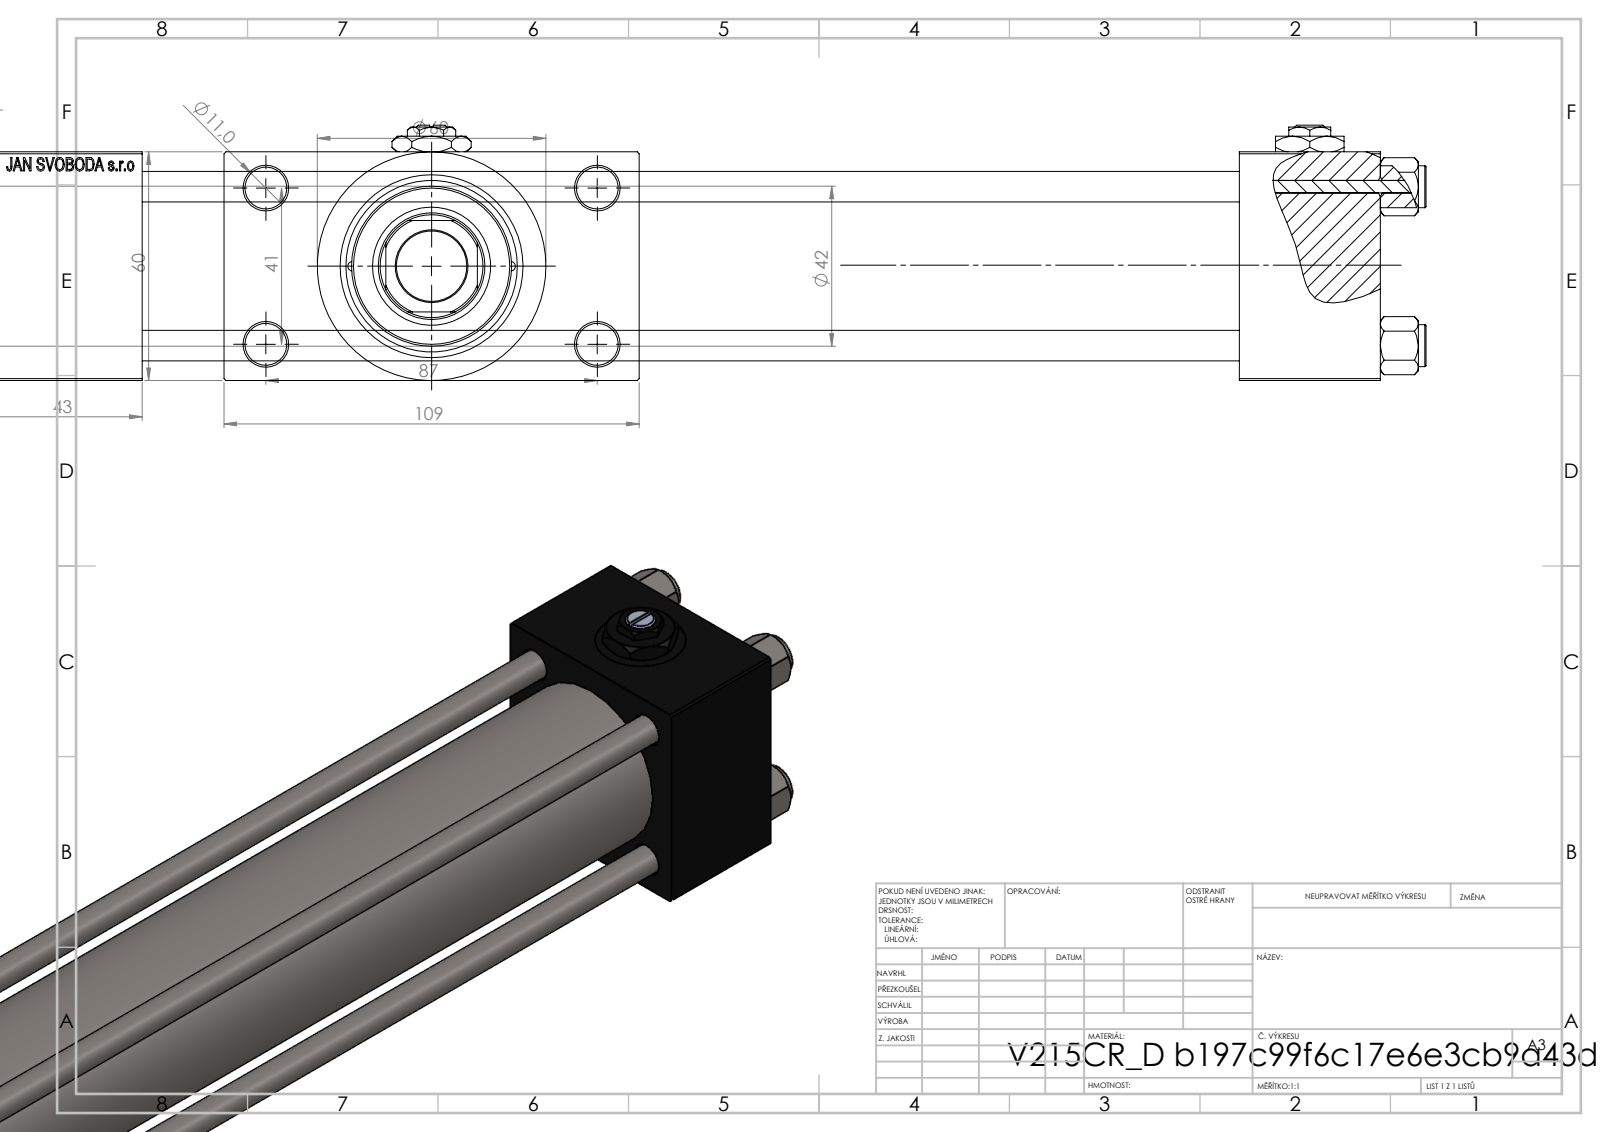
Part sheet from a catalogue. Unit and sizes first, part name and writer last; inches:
Units: inches
Overall size (bounding box): 16.339 × 4.291 × 2.638
Round holes (diameter × count): ⌀0.315 ×4, ⌀0.433 ×4, ⌀0.276 ×3, ⌀0.656 ×3, ⌀0.945 ×3, ⌀0.098 ×2, ⌀0.728 ×1, ⌀1.102 ×1, ⌀1.22 ×1, ⌀1.575 ×1, ⌀1.772 ×1
Round bosses / shafts (diameter × count): ⌀0.433 ×4, ⌀2.362 ×1, ⌀1.811 ×1, ⌀1.654 ×1
Partial cylindrical surfaces — rounded edges, fillets, slot ends (radius × count): R0.531 ×1
Main face-to-face distances: 2.362, 0.965, 11.339, 3.327, 1.457, 12.795, 14.488, 13.031, 1.693, 4.291
Hole centre spacings: 0.821, 0.892, 1.161, 1.206, 1.642, 1.832, 1.856, 1.893
Volume: 49.31 in³ · Surface area: 366.3 in²
Bodies: 12 solids, 1167 faces (526 planar, 99 cylindrical, 542 other)
Part name (STEP PRODUCT): Zatka_pro_OIL_PORT; V215_VC_A; V215CR_VCP_D; V215CR_D_Body (+2 more)
STEP written by: SolidWorks 2019 (CONFIG_CONTROL_DESIGN)
